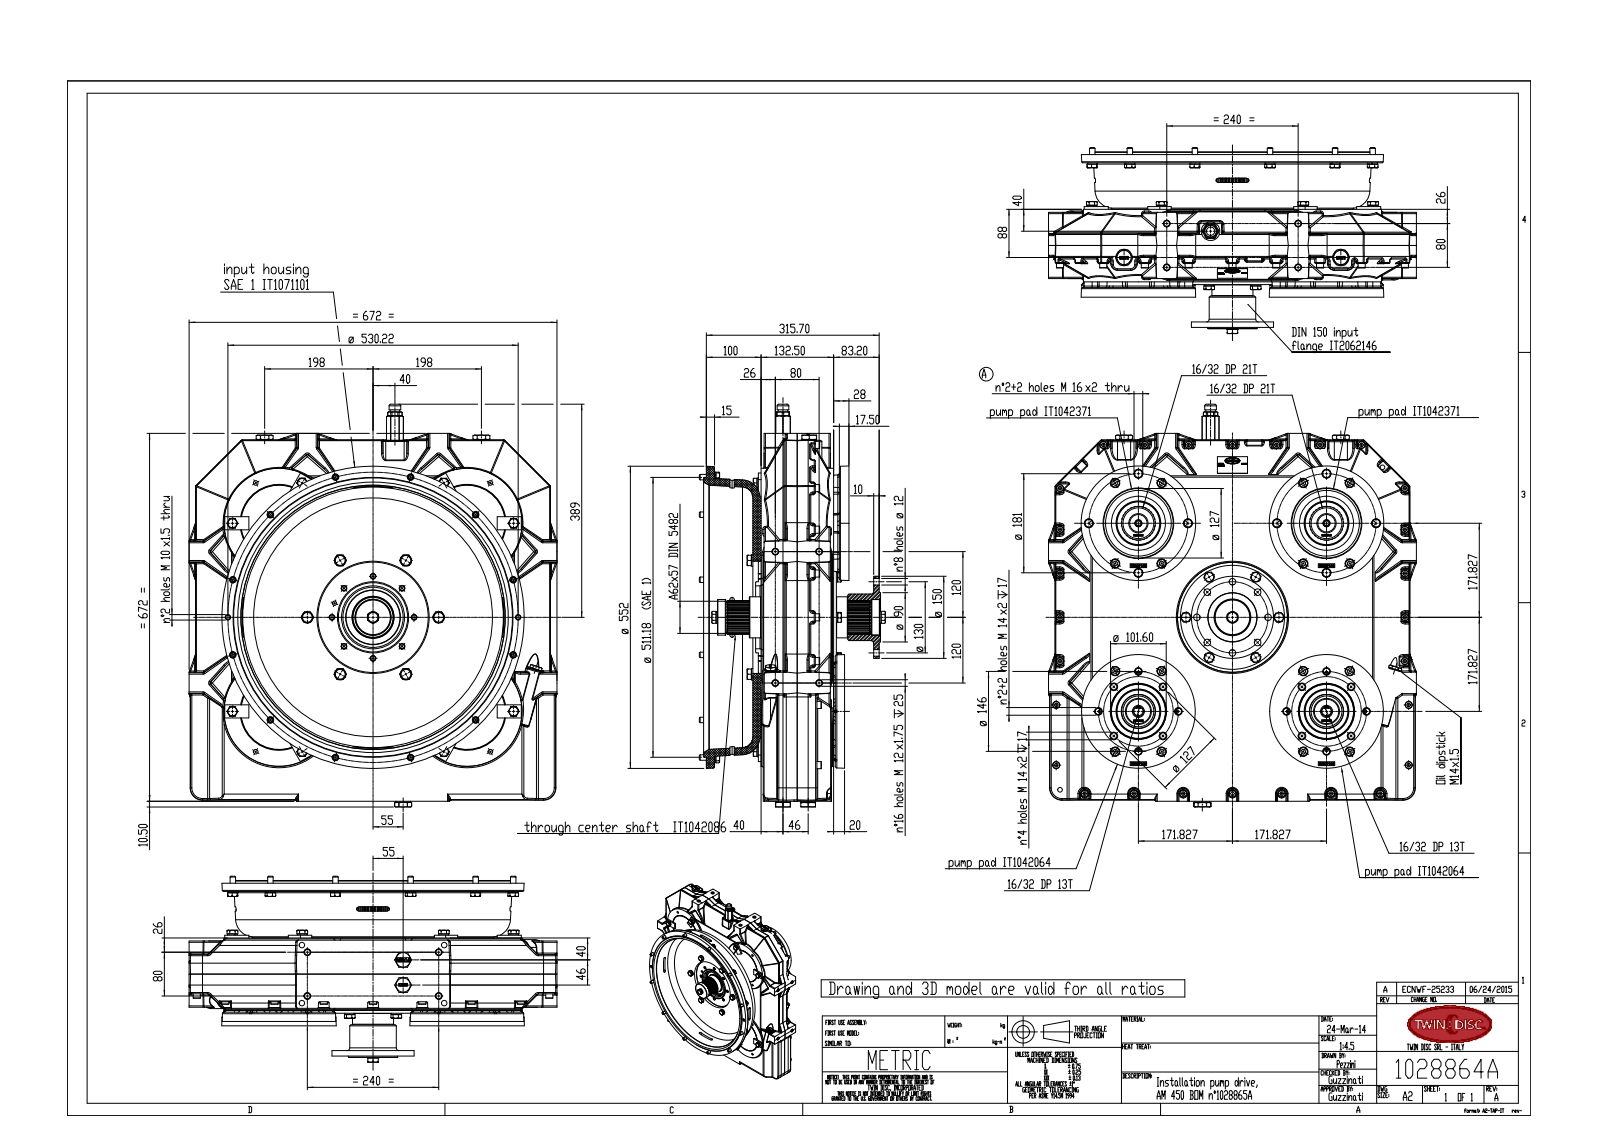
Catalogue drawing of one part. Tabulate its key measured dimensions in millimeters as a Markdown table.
| quantity | value |
| --- | --- |
| part name | IT1042086_rev02-installation; ITam450-006_rev00-installation; ITam450-002_rev00-installation; IT2062146_rev00-installation (+8 more) |
| STEP written by | SolidWorks 2007 (AUTOMOTIVE_DESIGN) |
| units | millimeters |
| bodies | 120 solids, 11171 faces (3878 planar, 3622 cylindrical, 3671 other) |
| overall size | 735.8 × 672 × 339.8 |
| volume | 10 320 000 mm³ |
| surface area | 4 841 000 mm² |
| round holes (diameter × count) | 8.5 × 70, 12 × 45, 10.2 × 41, 11 × 20, 17 × 16, 16 × 15, 10 × 12, 12.2 × 9, 13 × 9, 14 × 9, 10.5 × 6, 2 × 4 |
| round bosses / shafts (diameter × count) | 10 × 40, 13 × 28, 8 × 28, 16.2 × 27, 18.1 × 26, 14 × 17, 16 × 16, 21.1 × 9 |
| partial cylindrical surfaces (radius × count) | 2.5 × 324, 2 × 106, 0.45 × 58, 26.41 × 58, 3 × 36, 1.5 × 27, 5 × 24, 10 × 6 |
| main face-to-face distances | 66, 128.5, 4, 15, 143.5, 62.5, 66.5, 132.5, 19, 124.5 |
| hole center spacings | 85, 120, 178.39, 57.4, 75, 106.89, 138.58, 197.23 |
